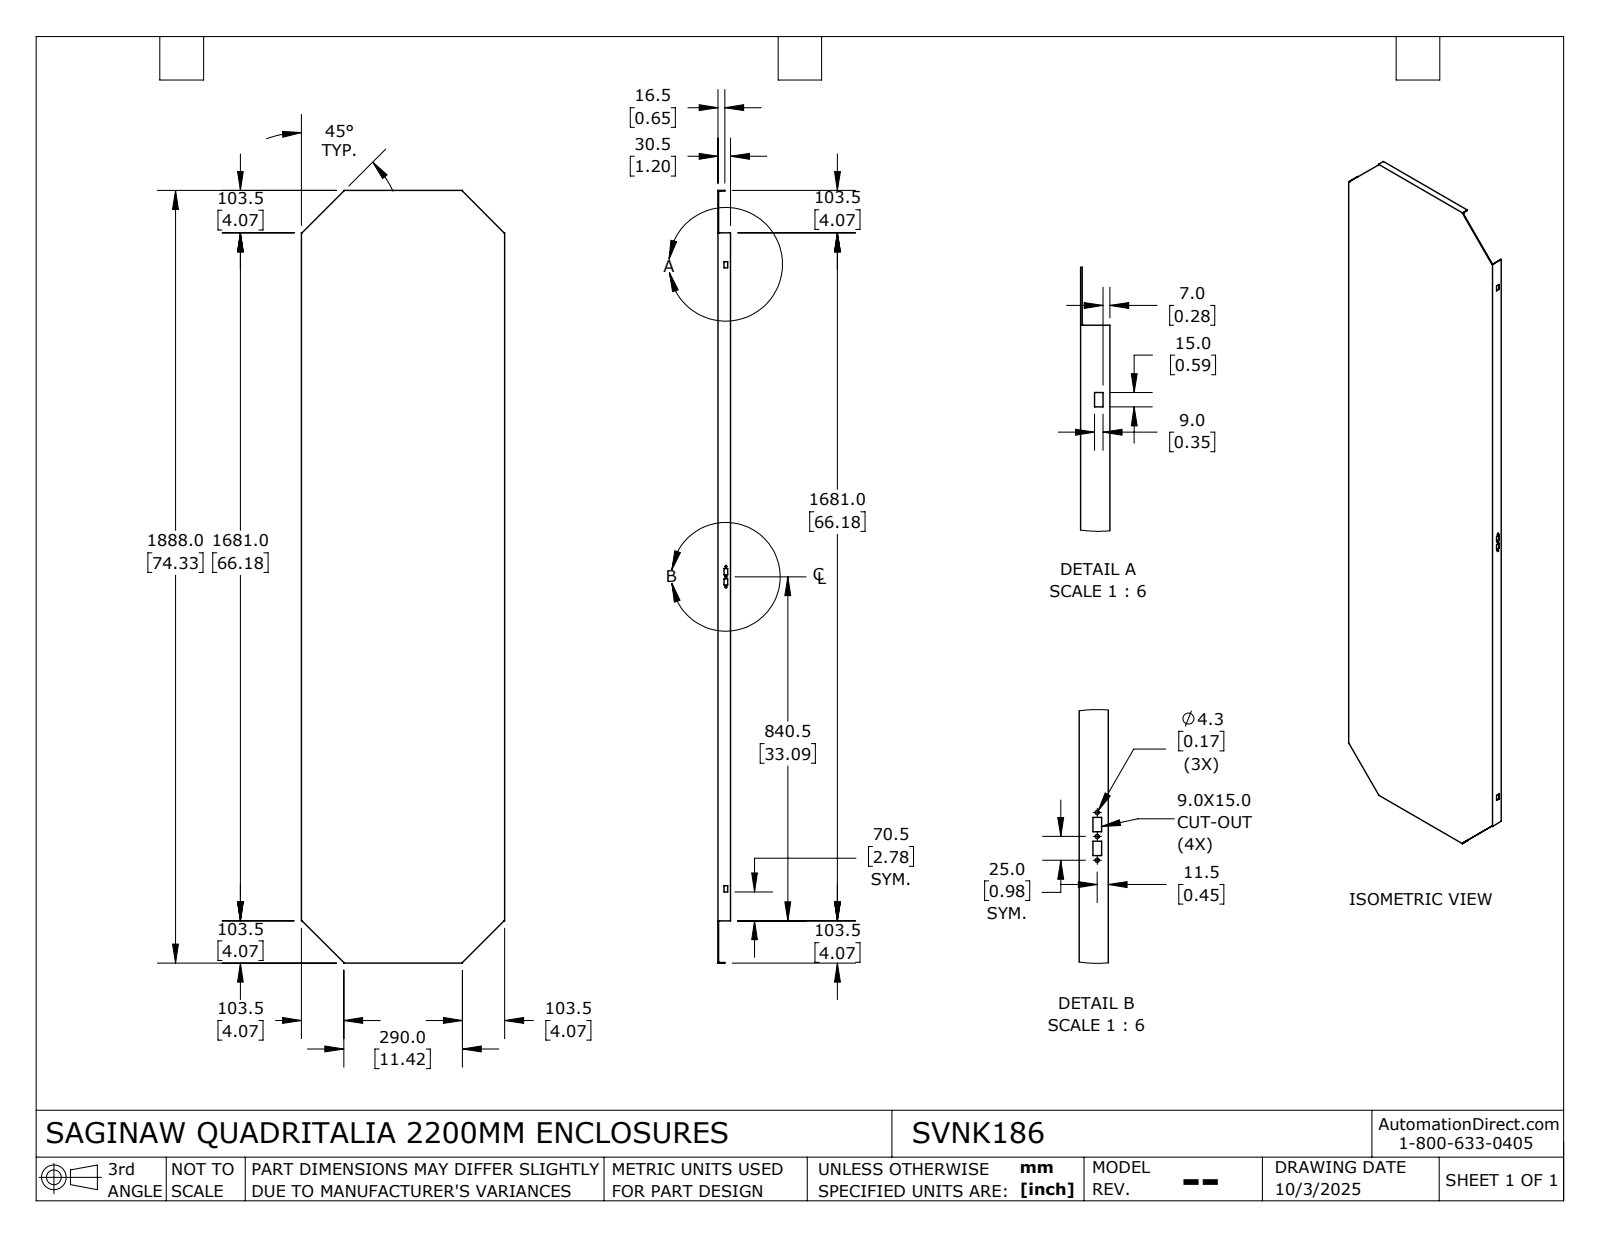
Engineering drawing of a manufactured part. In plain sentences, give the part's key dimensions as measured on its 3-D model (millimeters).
The part is named "SVNK186". Its 3-D file was written by "SolidWorks 2024 (AUTOMOTIVE_DESIGN)". It is 1 solid with 76 faces: 58 planar, 10 cylindrical and 8 other. Overall it measures 1888 by 497 by 30.5 millimeters. Its volume is 1 532 000 cubic millimeters and its surface area 2 050 000 square millimeters. Round holes: 3 of diameter 4.25. The main face-to-face distances are 1.5, 495.5, 497, 494, 1886.5, 30.5, 29, 1888, 1885, 15. The hole center spacings are 25, 50.
